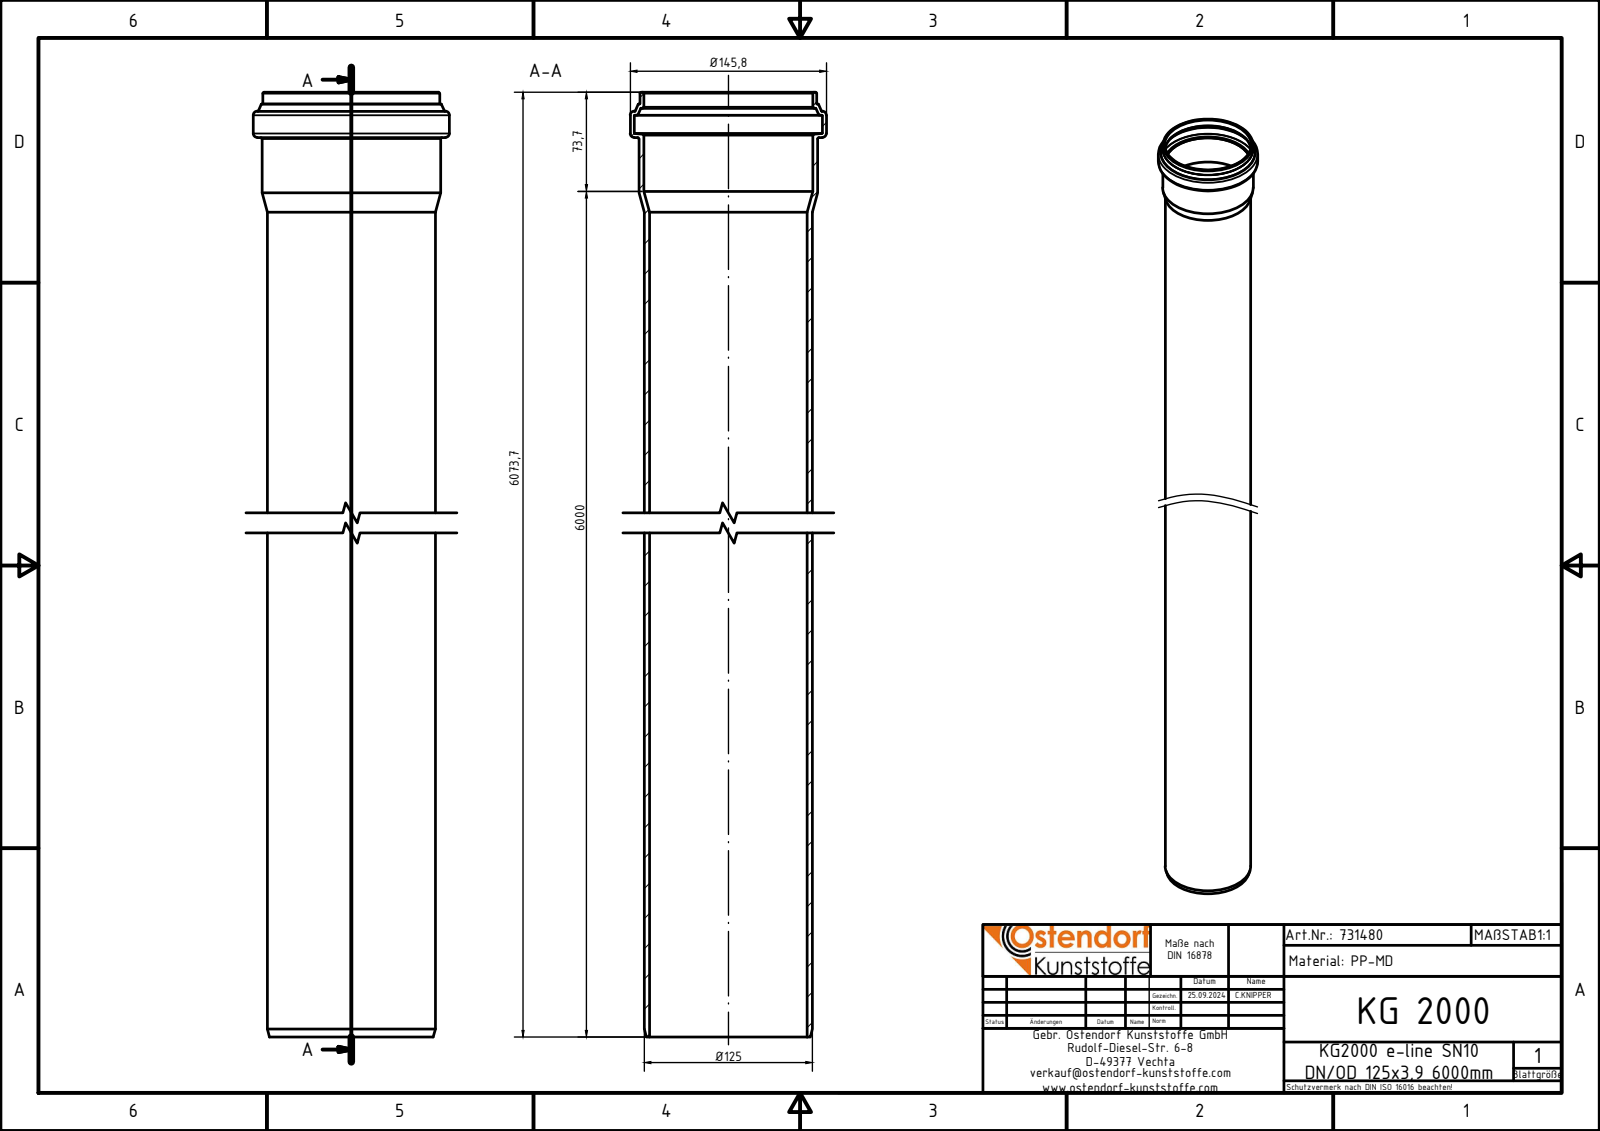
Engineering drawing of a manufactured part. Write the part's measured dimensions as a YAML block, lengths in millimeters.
part_name: "731480z"
step_written_by: "Autodesk Inventor 2024 (AUTOMOTIVE_DESIGN)"
units: millimeters
bodies: {solids: 1, faces: 35, planar: 5, cylindrical: 8, other: 22}
overall_size: [6073.7, 145.8, 145.8]
volume: 9016000
surface_area: 4637000
round_holes:
  - {diameter: 117.2, count: 1}
  - {diameter: 125.5, count: 1}
  - {diameter: 139.8, count: 1}
round_bosses_or_shafts:
  - {diameter: 145.8, count: 1}
  - {diameter: 132.7, count: 1}
  - {diameter: 131.5, count: 1}
  - {diameter: 125, count: 1}
face_to_face_distances: [6040, 6073.7, 33.7, 6064.87, 24.87, 8.83, 6059.5, 19.5, 5.37, 14.2]
